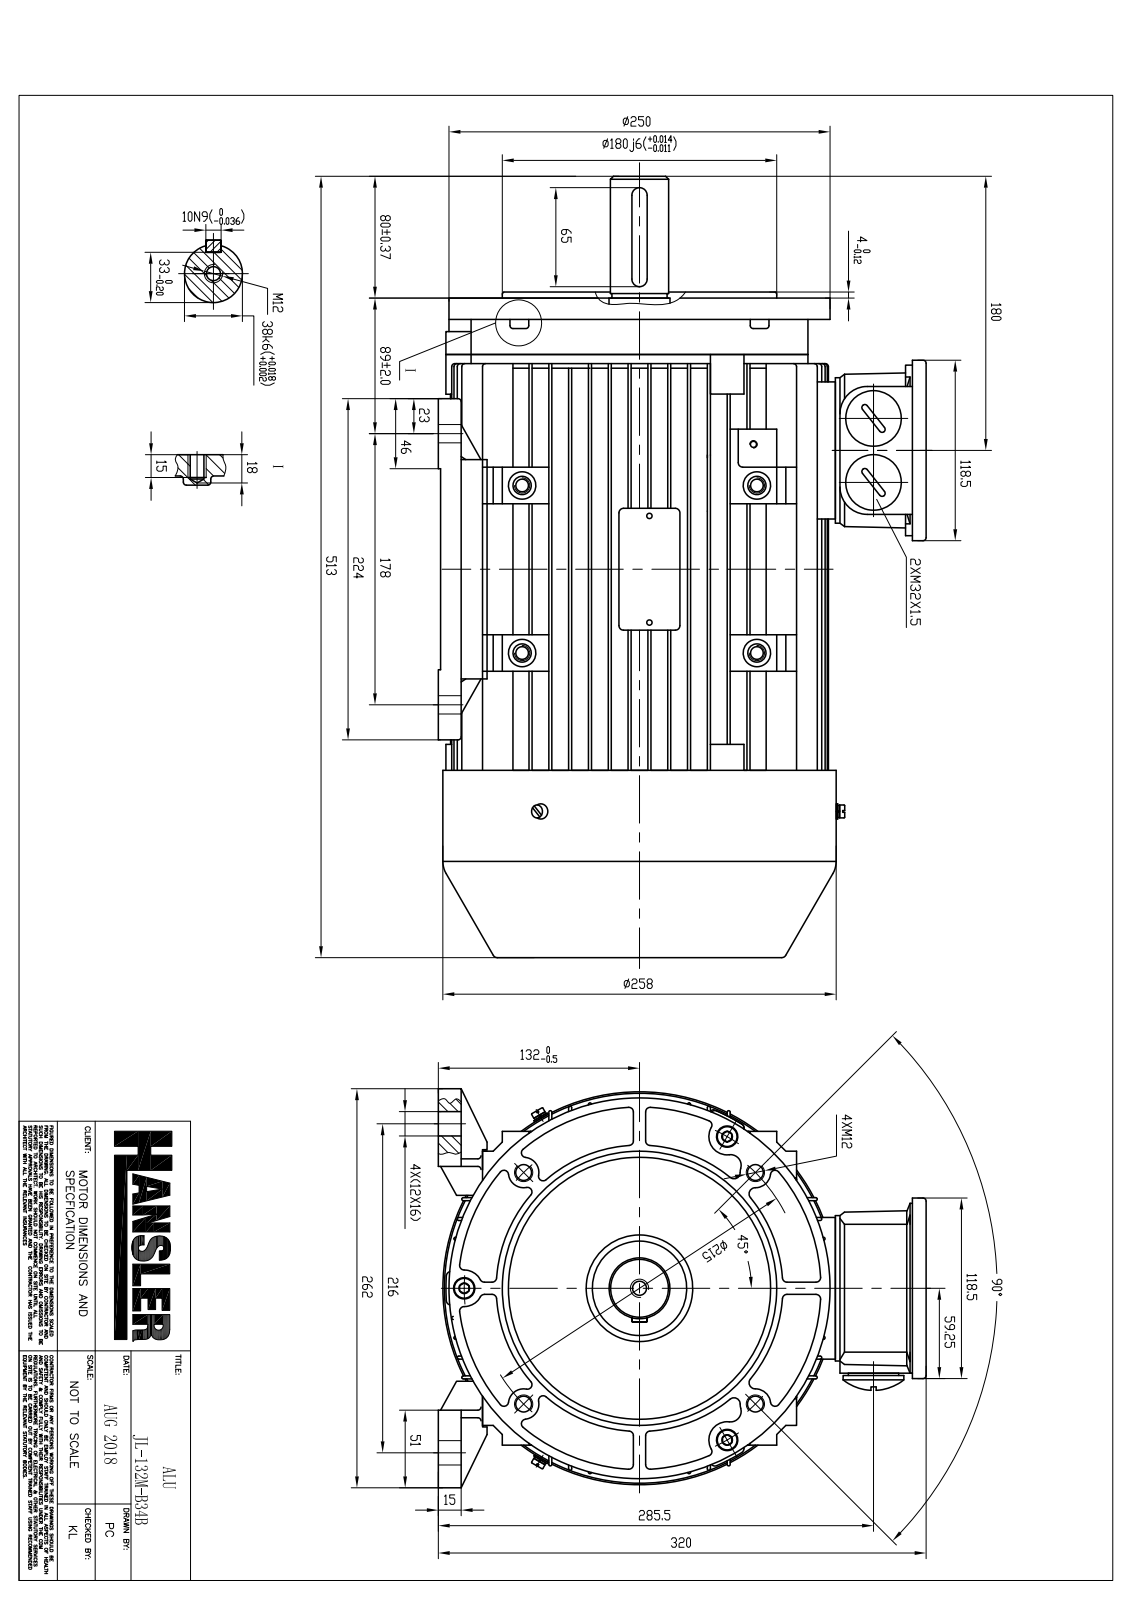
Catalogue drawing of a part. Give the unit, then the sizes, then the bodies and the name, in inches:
Units: inches
Overall size (bounding box): 20.197 × 12.717 × 10.367
Round holes (diameter × count): ⌀0.197 ×23, ⌀0.394 ×14, ⌀0.228 ×10, ⌀0.709 ×8, ⌀0.433 ×6, ⌀0.189 ×4, ⌀0.207 ×4, ⌀0.209 ×4, ⌀0.315 ×4, ⌀0.422 ×4, ⌀0.472 ×4, ⌀0.512 ×4
Round bosses / shafts (diameter × count): ⌀0.63 ×8, ⌀0.472 ×8, ⌀0.176 ×8, ⌀0.189 ×6, ⌀0.7 ×4, ⌀0.669 ×4, ⌀0.394 ×4, ⌀0.309 ×4
Partial cylindrical surfaces — rounded edges, fillets, slot ends (radius × count): R0.02 ×816, R0.079 ×122, R0.118 ×60, R0.039 ×34, R0.157 ×34, R0.098 ×18, R0.236 ×18, R0.197 ×9
Main face-to-face distances: 0.512, 0.079, 1.024, 3.583, 0.433, 4.094, 0.591, 3.071, 0.945, 4.606
Hole centre spacings: 1.584, 2.268, 2.406, 3.096, 3.32, 2.242, 0.696, 0.709
Volume: 236.7 in³ · Surface area: 2 996 in²
Bodies: 57 solids, 5495 faces (3272 planar, 1785 cylindrical, 438 other)
Part name (STEP PRODUCT): JL-132M-B34B
STEP written by: SIEMENS PLM Software NX 12.0 (AP203_CONFIGURATION_CONTROLLED_3D_DESIGN_OF_MECHANICAL_PARTS_AND_ASSEMBLIES_MIM_LF)
